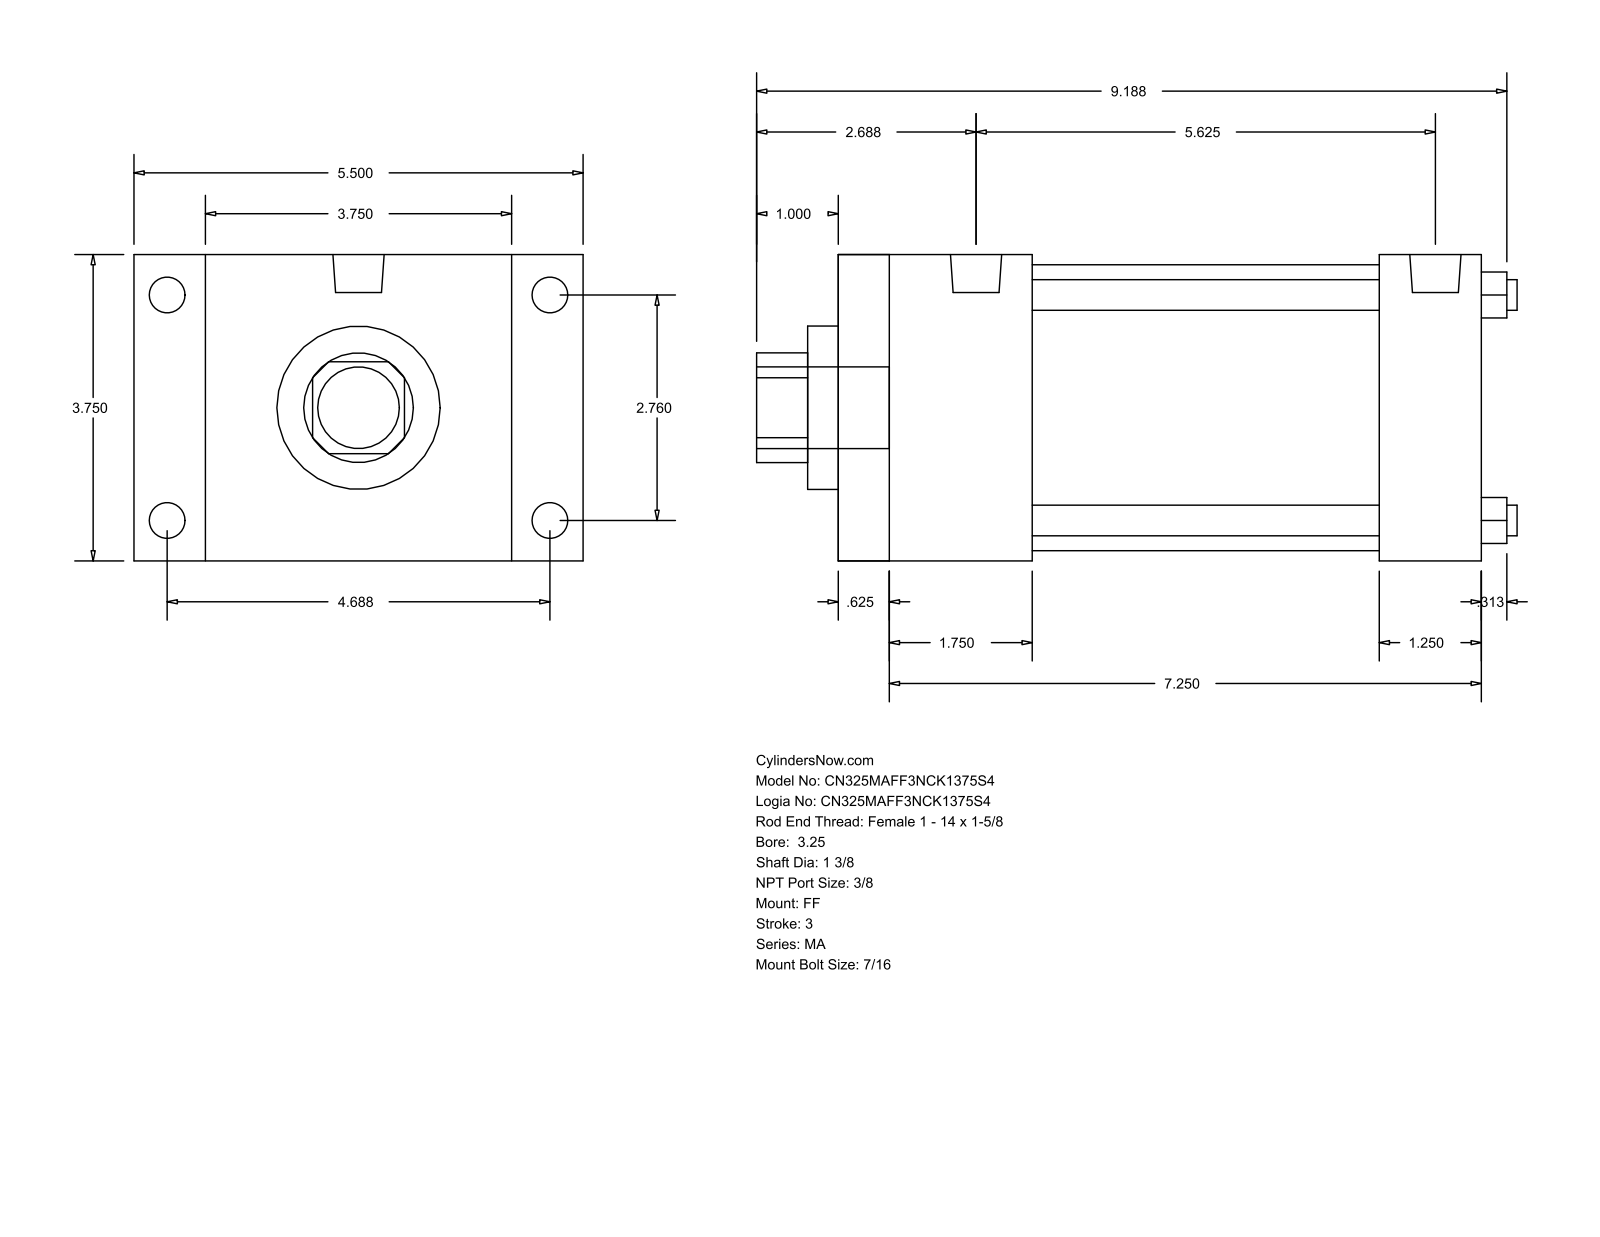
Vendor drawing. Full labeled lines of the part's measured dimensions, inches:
Part name (STEP PRODUCT): MA_FF__0325_1.375
STEP written by: GSSL Pune (CONFIG_CONTROL_DESIGN)
Units: inches
Bodies: 0 solids, 92 faces (64 planar, 28 cylindrical, 0 other)
Overall size (bounding box): 9.313 × 5.5 × 3.75
Round holes (diameter × count): ⌀0.375 ×4, ⌀1.375 ×1, ⌀2 ×1, ⌀3.5 ×1
Round bosses / shafts (diameter × count): ⌀0.437 ×8, ⌀0.627 ×2, ⌀1 ×1
Partial cylindrical surfaces — rounded edges, fillets, slot ends (radius × count): R0.672 ×1
Main face-to-face distances: 3.75, 7.875, 0.625, 7.25, 0.875, 4.625, 2.375, 6.625, 1.75, 6
Hole centre spacings: 1.952, 2.76, 3.903
